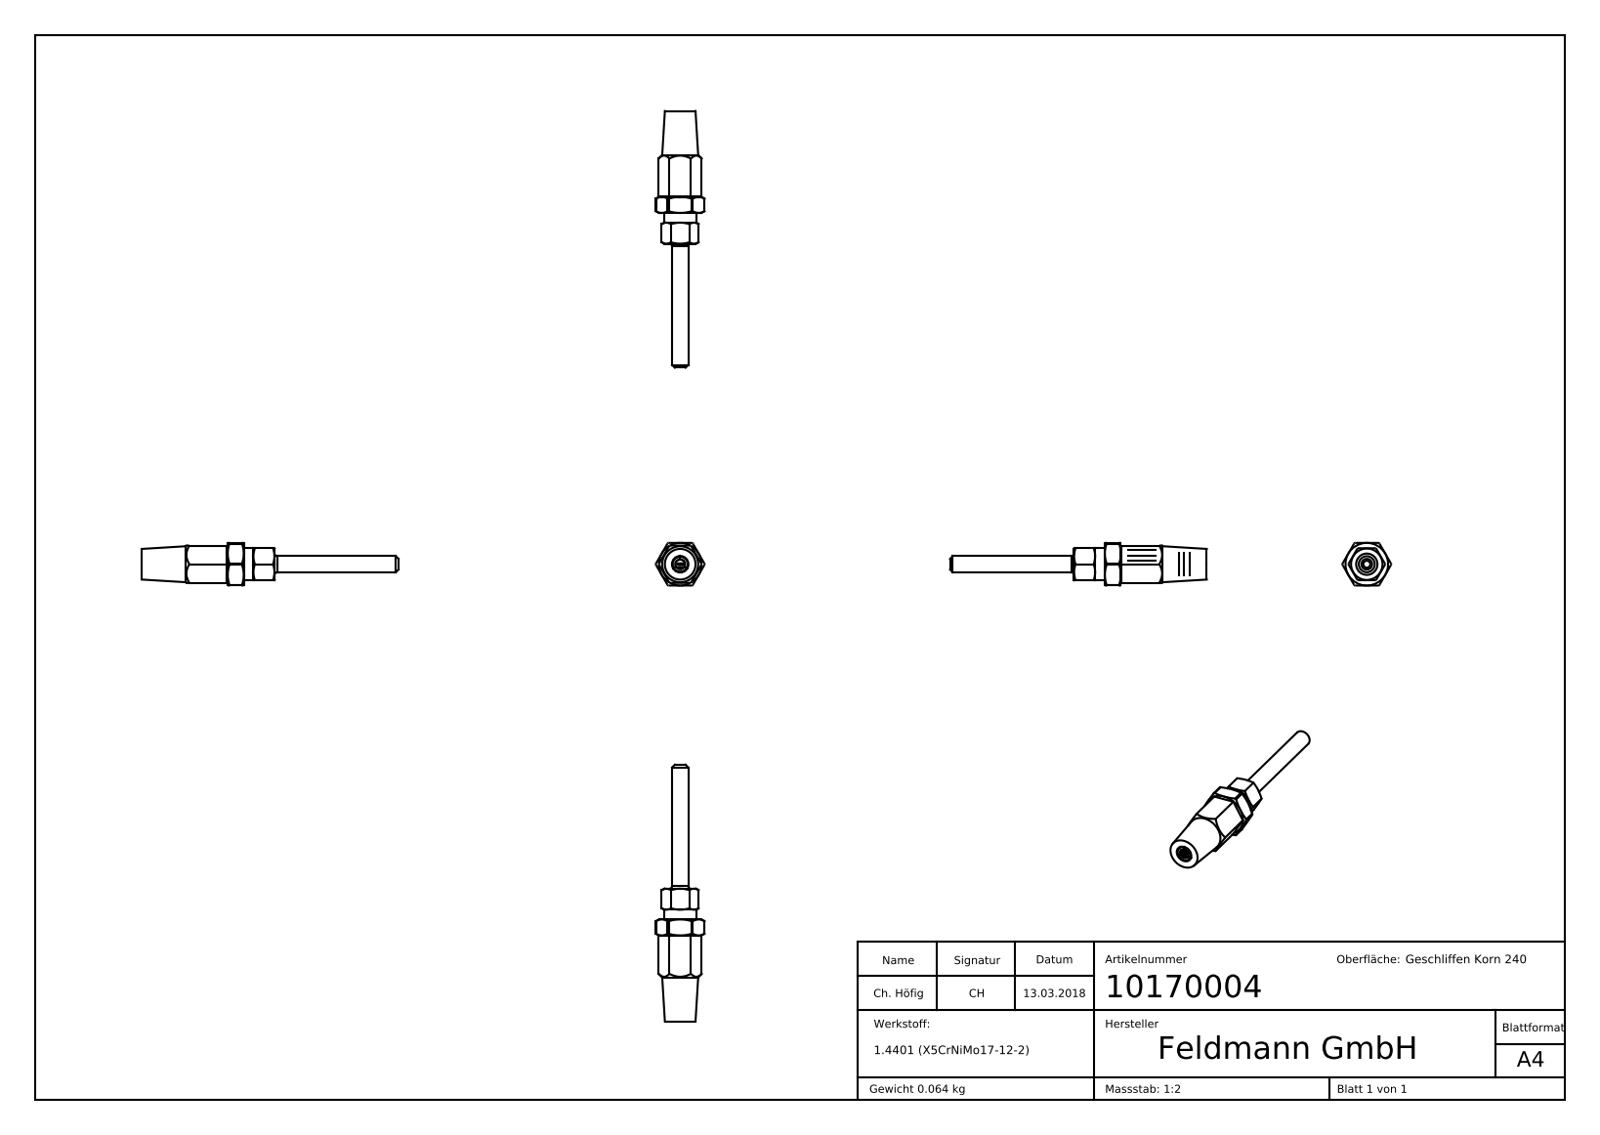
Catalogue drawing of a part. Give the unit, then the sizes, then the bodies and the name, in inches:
Units: inches
Overall size (bounding box): 3.793 × 0.721 × 0.63
Round holes (diameter × count): ⌀0.102 ×1, ⌀0.138 ×1, ⌀0.197 ×1, ⌀0.342 ×1, ⌀0.402 ×1
Round bosses / shafts (diameter × count): ⌀0.472 ×1, ⌀0.315 ×1, ⌀0.236 ×1
Partial cylindrical surfaces — rounded edges, fillets, slot ends (radius × count): R0.02 ×6
Main face-to-face distances: 0.551, 0.039, 0.512, 0.079, 0.591, 0.472, 0.63, 0.236, 0.728, 0.492
Volume: 0.486 in³ · Surface area: 10.19 in²
Bodies: 8 solids, 528 faces (150 planar, 123 cylindrical, 255 other)
Part name (STEP PRODUCT): 1017000X Teil5_10170004 Teil5; 1017000X Teil1_10170004 Teil1; 10170004; 1017000X Teil4_10170004 Teil4 (+3 more)
STEP written by: SolidWorks 2015 (CONFIG_CONTROL_DESIGN)
